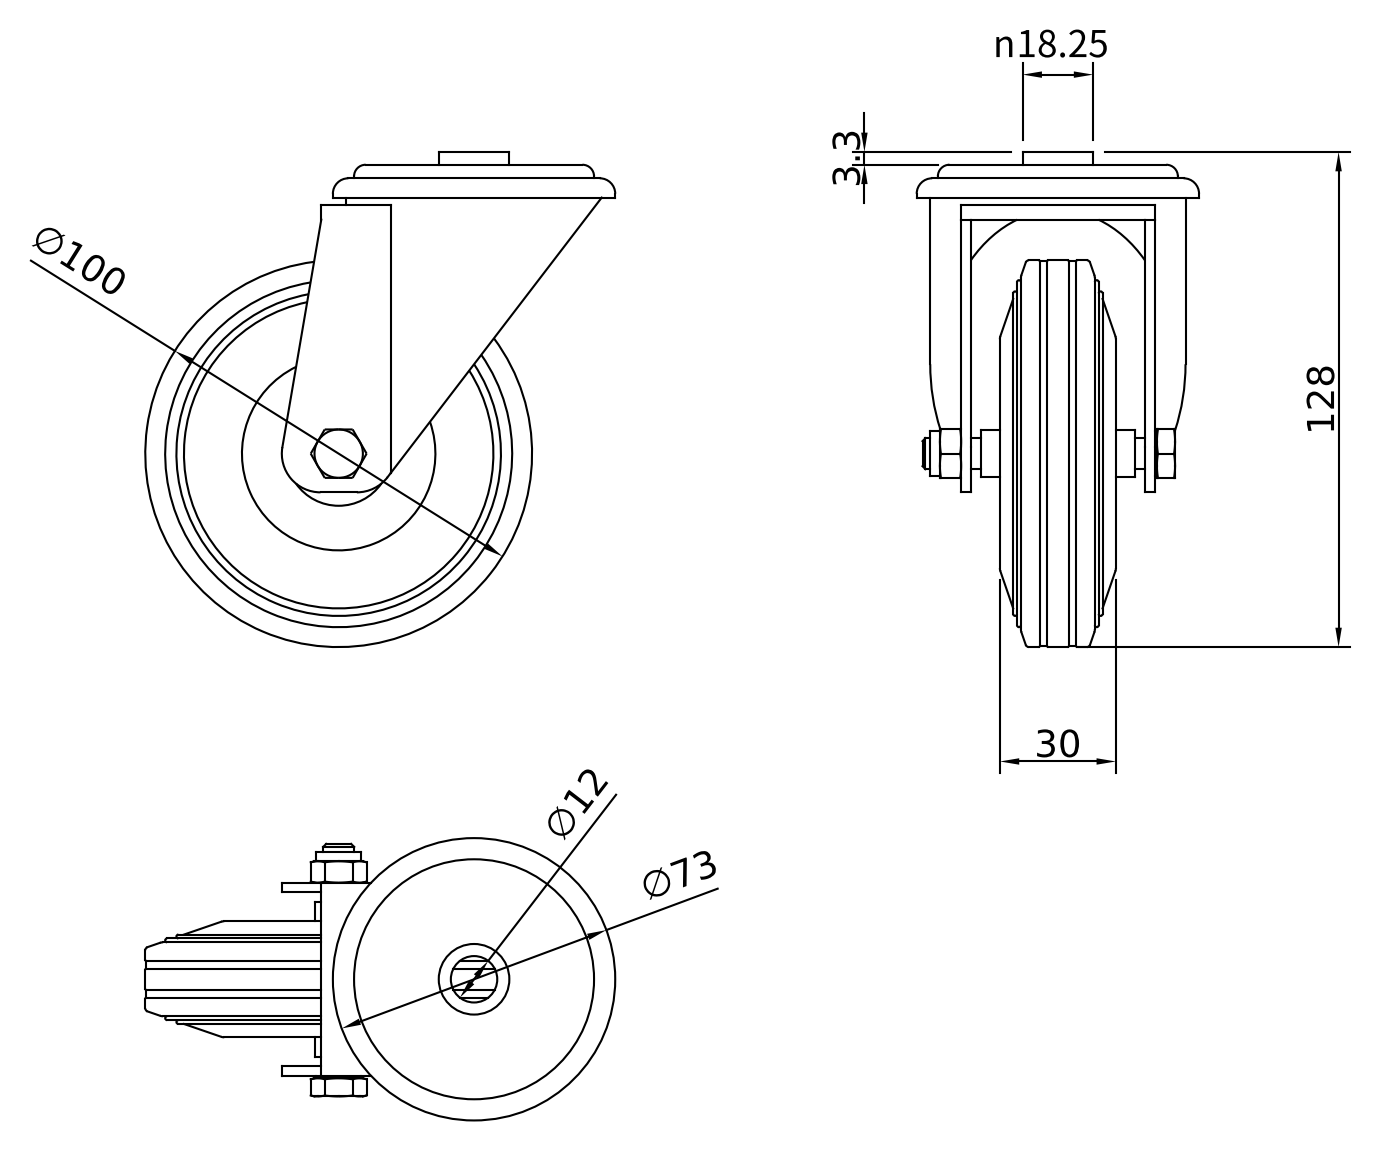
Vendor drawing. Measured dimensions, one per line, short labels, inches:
name: CRUST0000197; 440000025833; 440000025832; 440000025831
written by: Autodesk Inventor 2022 (AUTOMOTIVE_DESIGN)
unit: in
bodies: 3 solids, 128 faces (50 planar, 25 cylindrical, 53 other)
size: 5.039 × 4.783 × 2.874
volume: 14.68 in³; area: 87.89 in²
holes: 2× ⌀0.472, 1× ⌀0.354, 1× ⌀2.402
bosses: 1× ⌀3.937, 1× ⌀3.917, 1× ⌀2.874, 1× ⌀2.598, 1× ⌀2.443, 1× ⌀0.719, 1× ⌀0.458, 1× ⌀0.315
rounds: 2× R0.394
face distances: 0.098, 1.87, 0.421, 1.575, 0.394, 0.295, 1.476, 1.772, 1.969, 0.569
